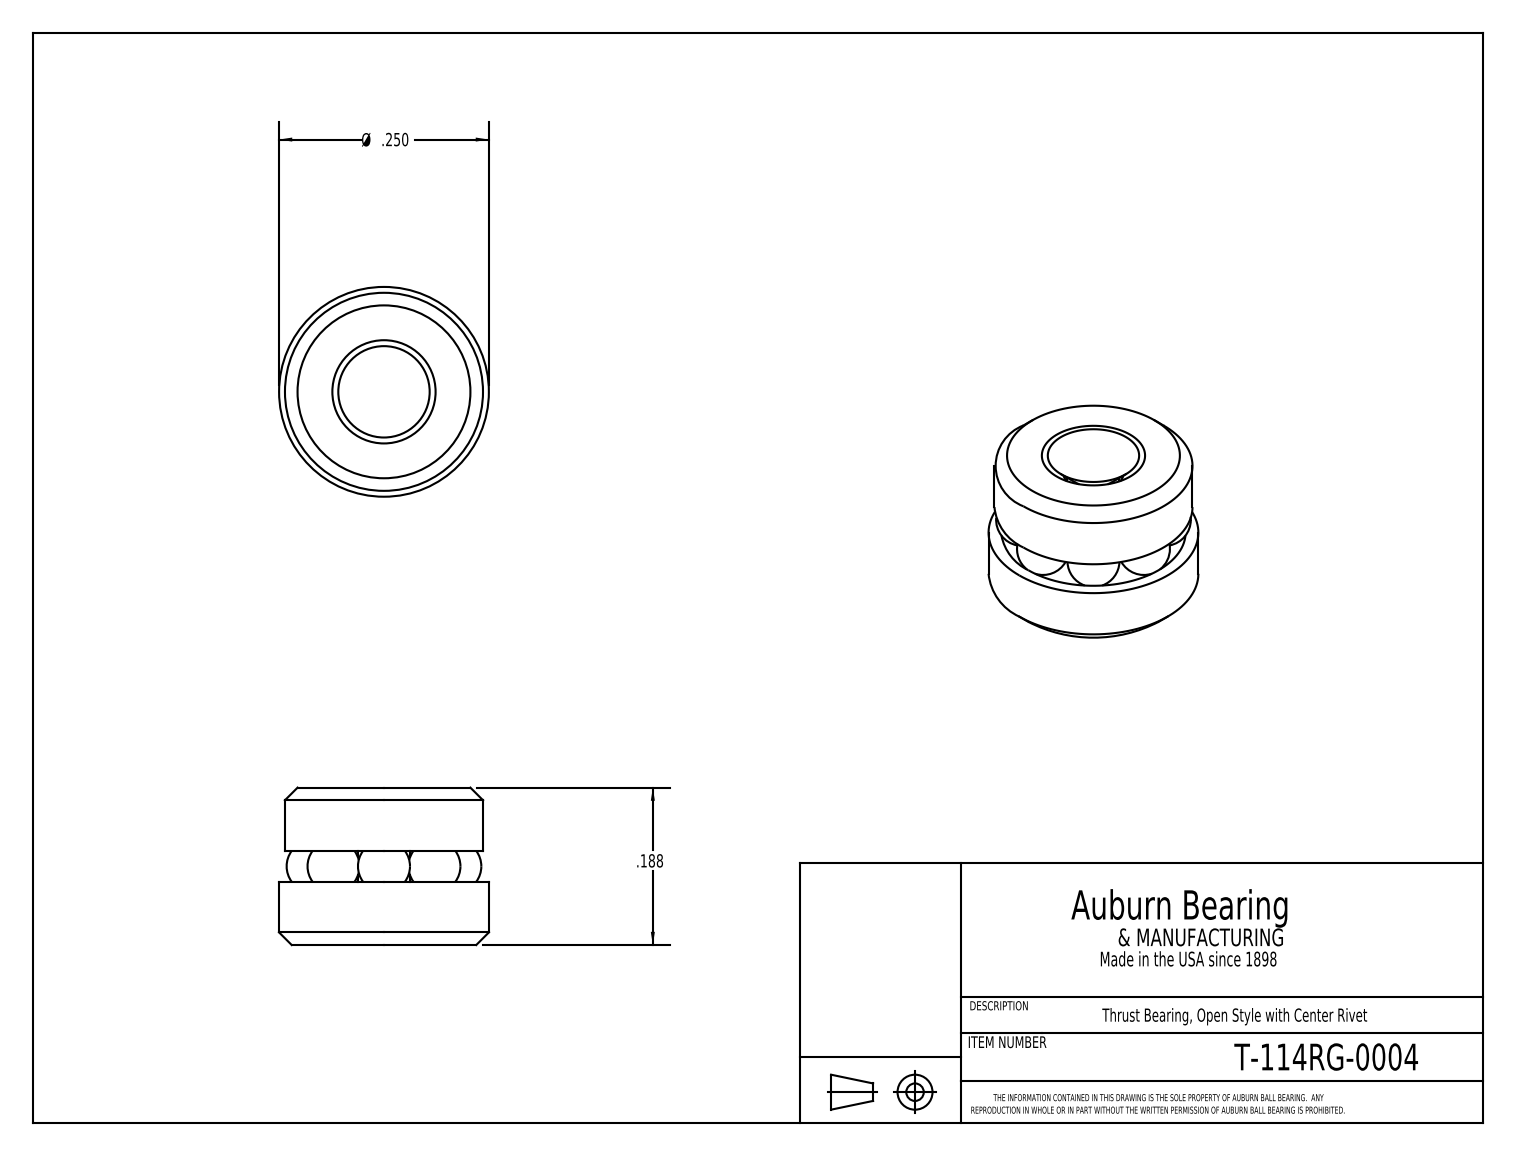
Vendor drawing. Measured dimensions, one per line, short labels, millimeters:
name: T-114RG_T-114RG-0004
written by: SolidWorks 2016 (CONFIG_CONTROL_DESIGN)
unit: mm
bodies: 11 solids, 29 faces (8 planar, 5 cylindrical, 16 other)
size: 6.4 × 6.4 × 4.8
volume: 100 mm³; area: 302 mm²
holes: 1× ⌀1.8
bosses: 1× ⌀6.4, 1× ⌀6, 1× ⌀1.6
face distances: 1.9, 2.8, 4.7, 0.9
